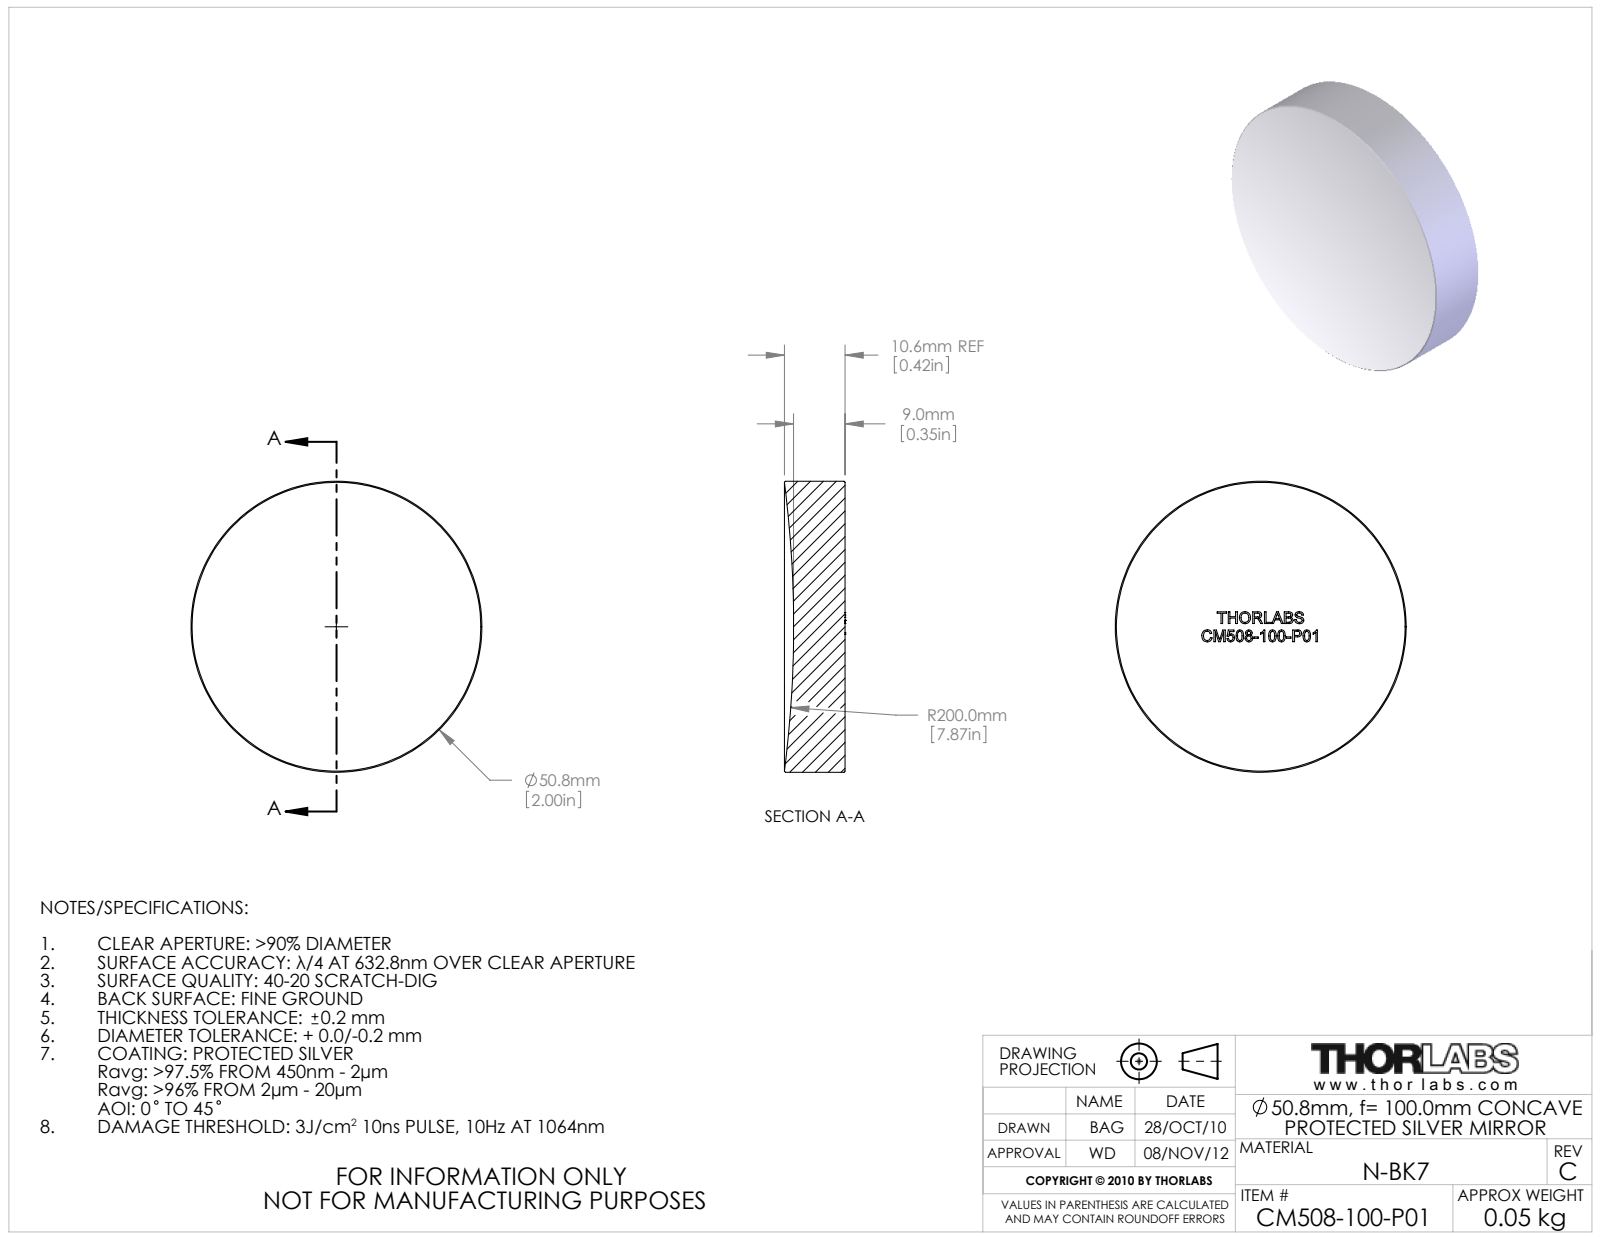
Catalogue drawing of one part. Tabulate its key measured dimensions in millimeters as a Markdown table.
| quantity | value |
| --- | --- |
| part name | 17572-E0W |
| STEP written by | SolidWorks 2009 (AUTOMOTIVE_DESIGN) |
| units | millimeters |
| bodies | 1 solid, 276 faces (141 planar, 2 cylindrical, 133 other) |
| overall size | 50.8 × 50.8 × 10.6 |
| volume | 19 880 mm³ |
| surface area | 5 716 mm² |
| round bosses / shafts (diameter × count) | 50.8 × 1 |
| main face-to-face distances | 2.1, 1.6, 5.5, 2.1, 3.8, 1, 2.5, 2.3, 3.1, 2.5 |
